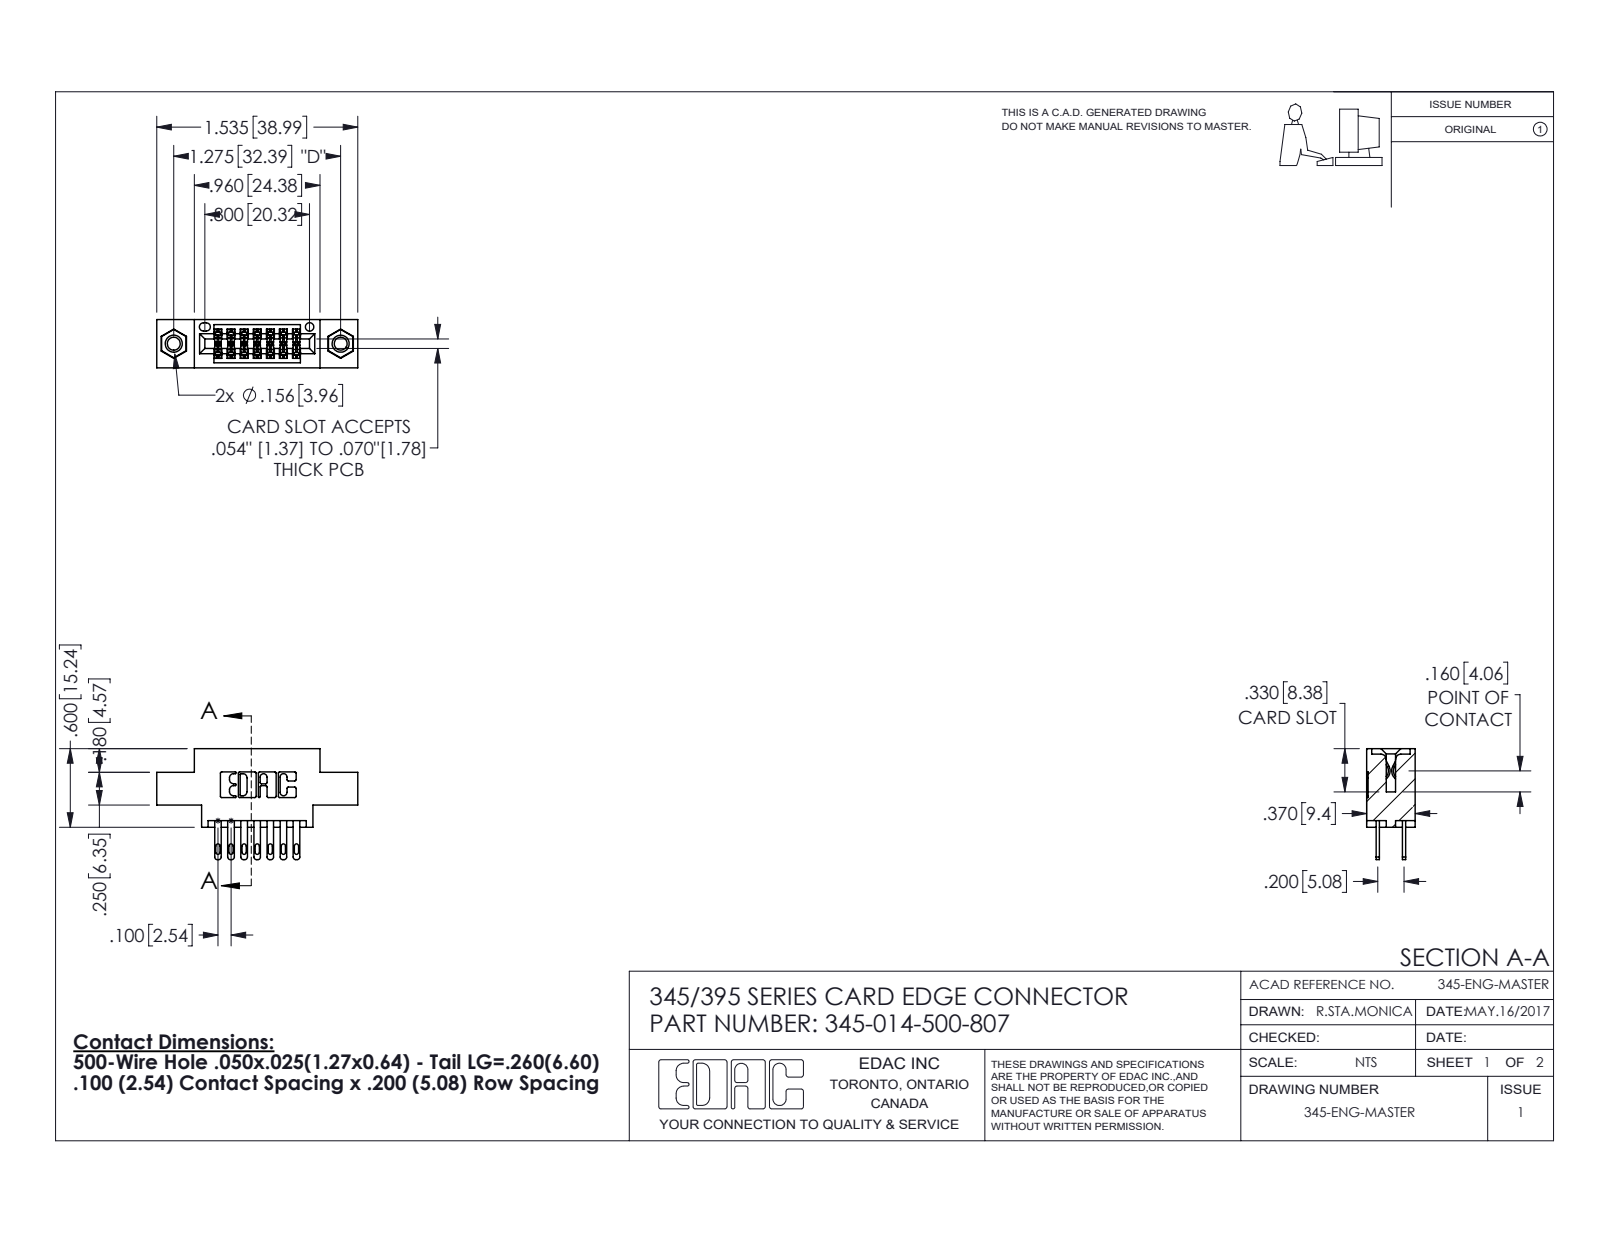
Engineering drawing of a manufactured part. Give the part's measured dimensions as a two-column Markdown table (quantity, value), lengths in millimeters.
| quantity | value |
| --- | --- |
| part name | 345-014-500-807; 345-292-001_345-293-100; 345-250-001_345-250-005-103; 345 Part_0.170 Offset - 0.156 Dia-TI |
| STEP written by | SolidWorks 2016 (CONFIG_CONTROL_DESIGN) |
| units | millimeters |
| bodies | 17 solids, 834 faces (494 planar, 324 cylindrical, 16 other) |
| overall size | 39 × 21.5 × 9.4 |
| volume | 3 380 mm³ |
| surface area | 4 630 mm² |
| round holes (diameter × count) | 2.5 × 2, 3.2 × 2, 4 × 2, 1.6 × 1 |
| round bosses / shafts (diameter × count) | 3.9 × 2 |
| partial cylindrical surfaces (radius × count) | 0.3 × 22, 0.2 × 21, 0.4 × 14, 0.5 × 14, 0.2 × 6, 0.8 × 6, 0.7 × 3, 0.4 × 2 |
| main face-to-face distances | 5.1, 1.8, 7.6, 9.4, 2.5, 2.5, 6.9, 0.6, 5.7, 7.6 |
| hole center spacings | 6.9, 26.5, 32.4 |
